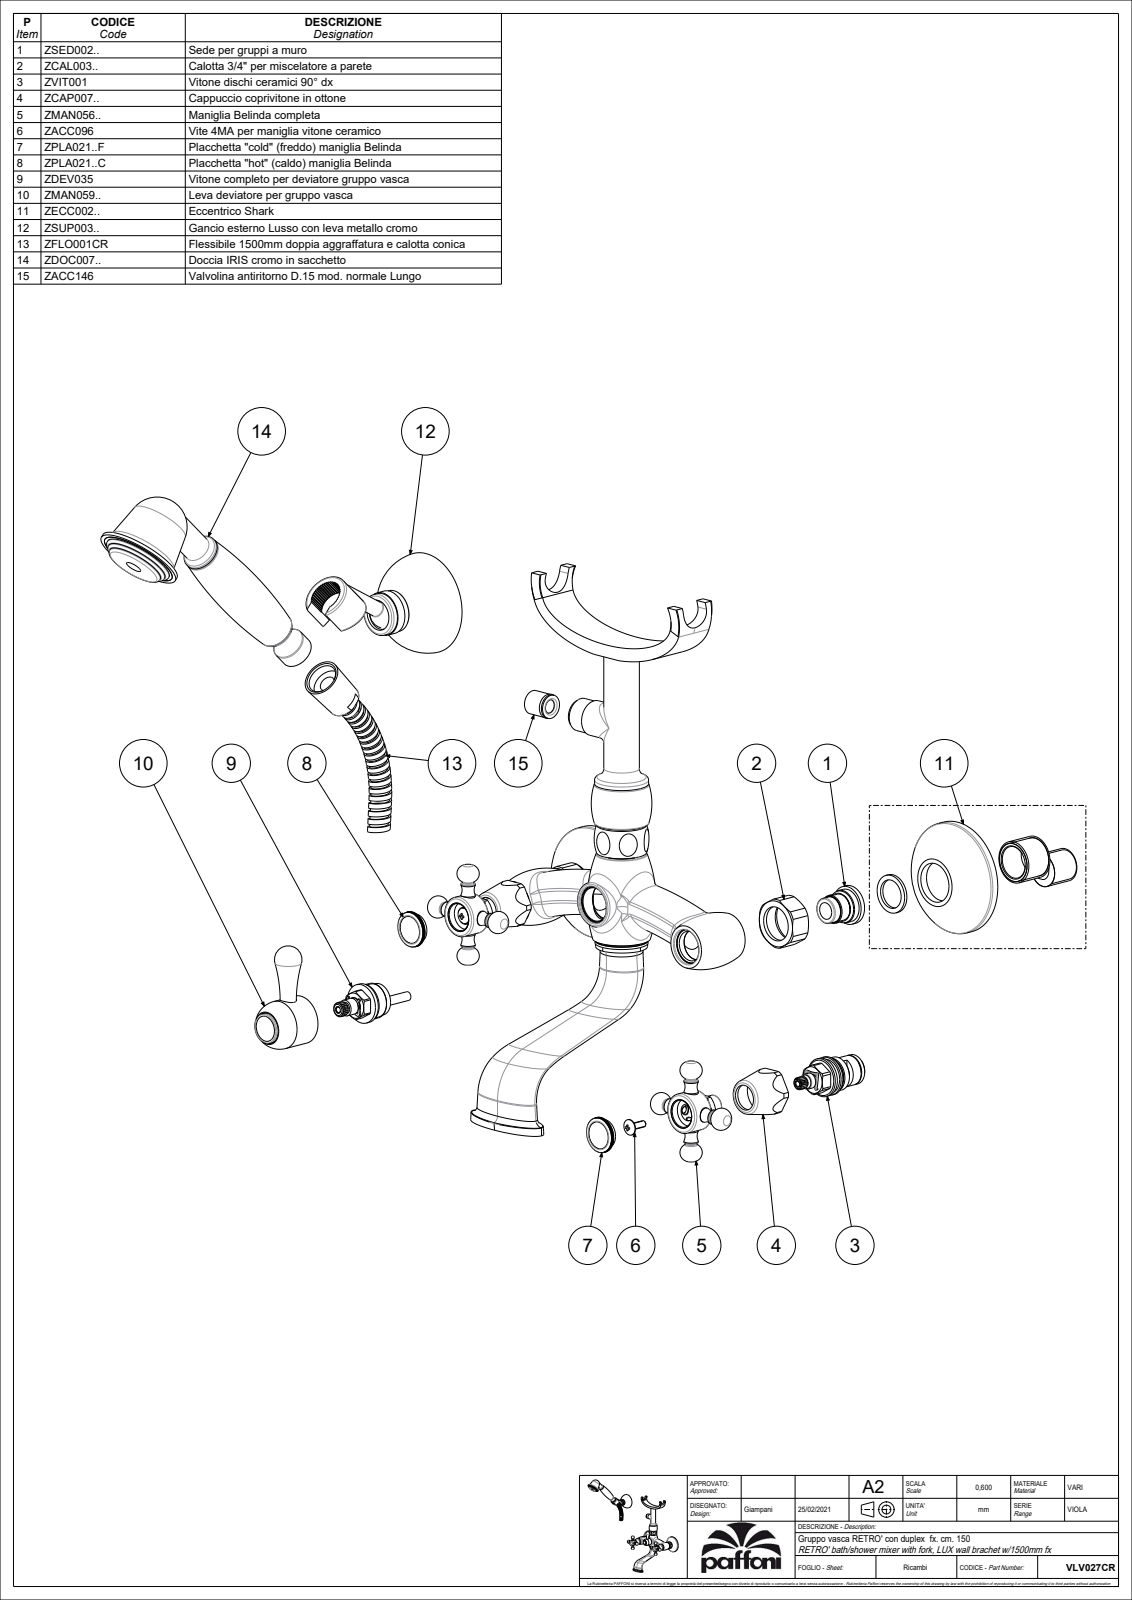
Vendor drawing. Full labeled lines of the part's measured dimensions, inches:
Part name (STEP PRODUCT): VLV027CR
STEP written by: CREO PARAMETRIC BY PTC INC, 2020044 (CONFIG_CONTROL_DESIGN)
Units: inches
Bodies: 7 solids, 1691 faces (668 planar, 447 cylindrical, 576 other)
Overall size (bounding box): 15.93 × 14.429 × 9.578
Volume: 40.98 in³ · Surface area: 288.5 in²
Round holes (diameter × count): ⌀0.846 ×3, ⌀0.906 ×3, ⌀0.949 ×3, ⌀0.618 ×2, ⌀0.657 ×2, ⌀0.733 ×2, ⌀0.748 ×2, ⌀0.827 ×2, ⌀1.051 ×2, ⌀0.571 ×1, ⌀0.591 ×1, ⌀0.945 ×1
Round bosses / shafts (diameter × count): ⌀0.551 ×3, ⌀0.354 ×3, ⌀0.276 ×3, ⌀2.756 ×2, ⌀0.984 ×2, ⌀0.866 ×2, ⌀0.512 ×2, ⌀2.087 ×1
Partial cylindrical surfaces — rounded edges, fillets, slot ends (radius × count): R0.138 ×2, R0.394 ×2, R0.433 ×2, R0.571 ×2, R0.61 ×2, R0.551 ×1
Main face-to-face distances: 1.732, 0.787, 0.915, 0.128, 1.043, 0.61, 0.945, 0.817, 1.398, 1.142
Hole centre spacings: 3.004, 5.906
